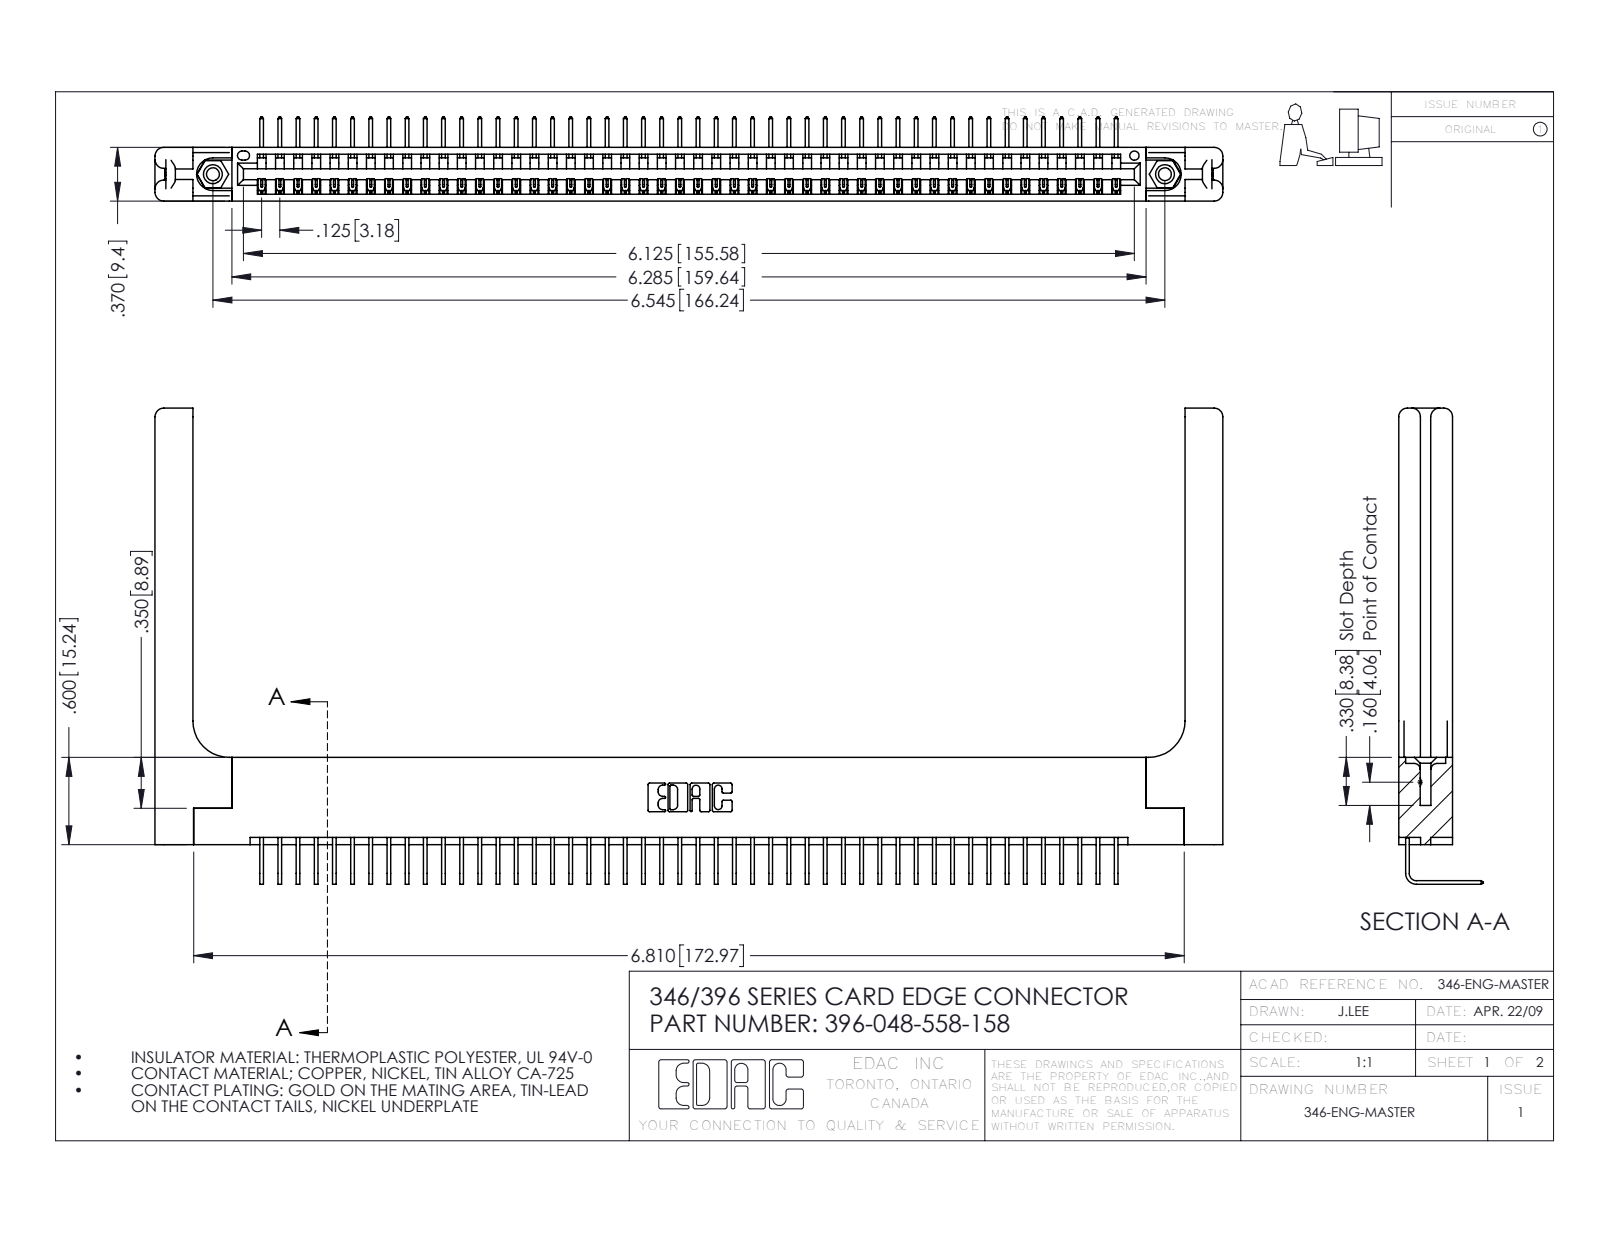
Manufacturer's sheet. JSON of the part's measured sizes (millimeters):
{"part_name": "396-048-558-158; 346-220-058_345-220-058; 345-292-001_558 Tail - 2; 346 Part_Flush Mounting Lugs - 0.156 Dia-TH (+1 more)", "step_written_by": "SolidWorks 2016 (CONFIG_CONTROL_DESIGN)", "units": "millimeters", "bodies": {"solids": 53, "faces": 3258, "planar": 2240, "cylindrical": 958, "other": 60}, "overall_size": [186.5, 83.1, 14.7], "volume_mm3": 25560, "surface_area_mm2": 28750, "round_holes": [[2.3, 2], [3.2, 2], [4, 2], [1.6, 1]], "round_bosses_or_shafts": [[3.9, 2]], "partial_cylinders_radius": [[0.2, 96], [0.3, 22], [1.5, 16], [0.2, 6], [0.8, 6], [0.7, 3], [0.8, 2], [0.8, 2]], "face_to_face_distances": [9.4, 8.2, 1.2, 1.8, 3.8, 3.8, 0.6, 7.6, 6.4, 5.6], "hole_center_spacings": [6.2, 160.9, 166.2]}
